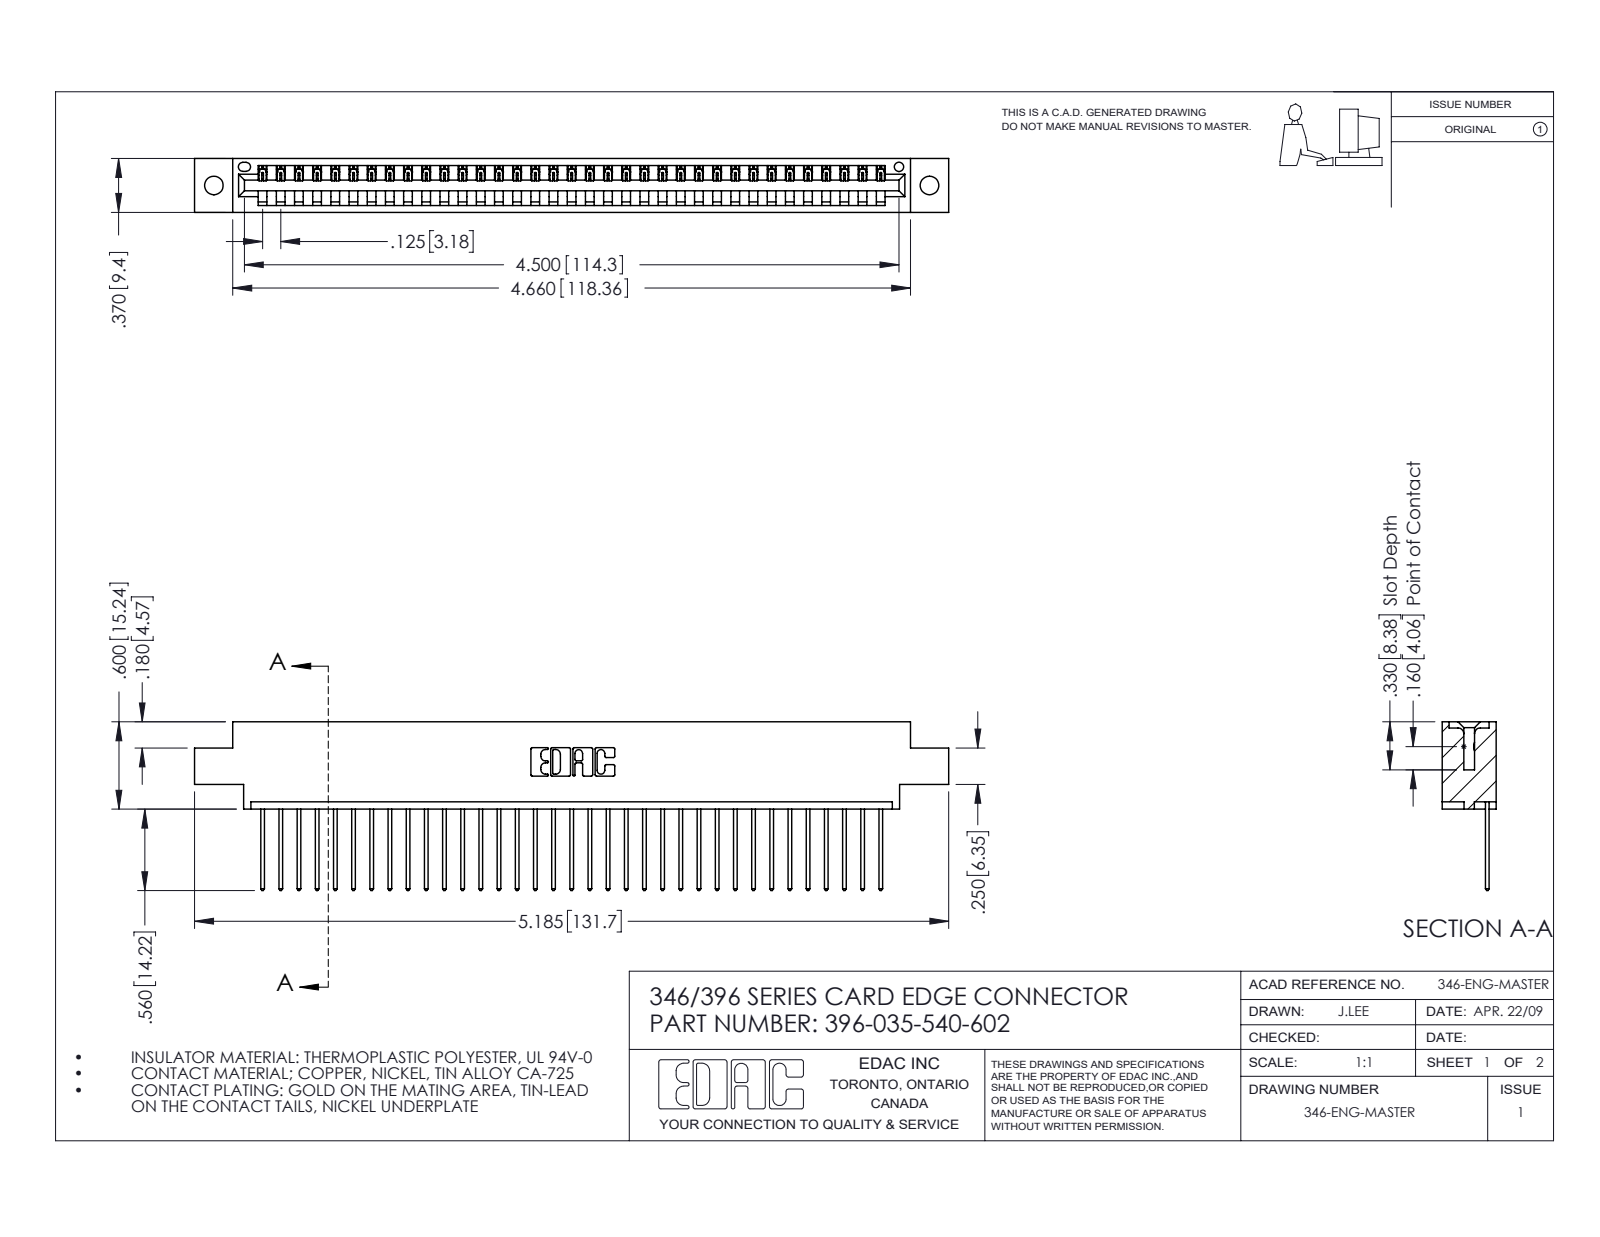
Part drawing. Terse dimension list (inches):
name: 346 Part_0.170 Offset - 0.128 Dia; 396-035-540-602; 345-292-001_345-293-140
written by: SolidWorks 2016 (CONFIG_CONTROL_DESIGN)
unit: in
bodies: 36 solids, 2156 faces (1480 planar, 676 cylindrical, 0 other)
size: 5.185 × 1.16 × 0.37
volume: 0.758 in³; area: 24.3 in²
holes: 2× ⌀0.128, 1× ⌀0.064
rounds: 70× R0.006, 70× R0.01, 22× R0.01, 6× R0.007, 6× R0.031, 3× R0.026, 2× R0.031, 2× R0.04
face distances: 0.048, 0.322, 0.37, 0.25, 0.072, 0.298, 0.025, 0.148, 0.222, 0.1
hole spacings: 0.246, 4.711, 4.92
